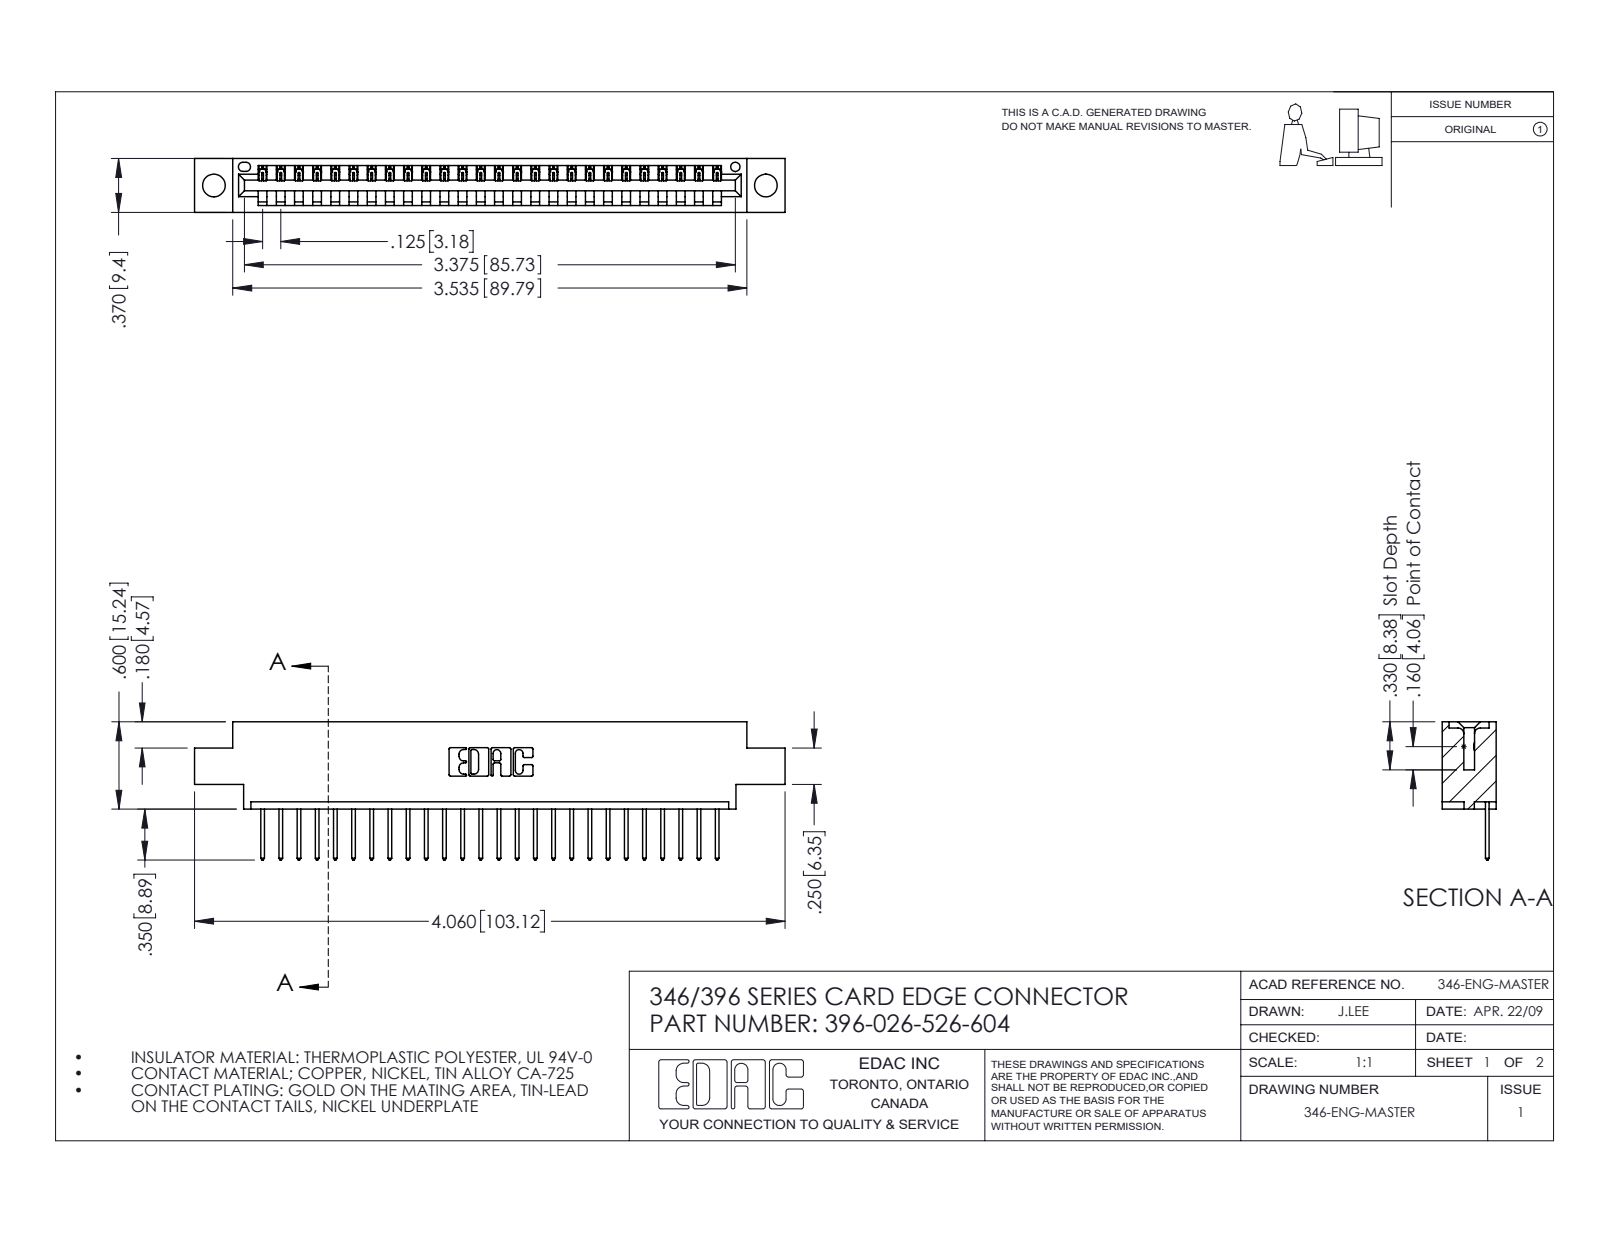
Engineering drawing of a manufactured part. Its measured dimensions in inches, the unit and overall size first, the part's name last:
Units: inches
Overall size (bounding box): 4.06 × 0.95 × 0.37
Round holes (diameter × count): ⌀0.156 ×2, ⌀0.064 ×1
Partial cylindrical surfaces — rounded edges, fillets, slot ends (radius × count): R0.006 ×52, R0.01 ×52, R0.01 ×22, R0.007 ×6, R0.031 ×6, R0.026 ×3, R0.031 ×2, R0.04 ×2
Main face-to-face distances: 0.048, 0.322, 0.37, 0.25, 0.072, 0.298, 0.025, 0.148, 0.222, 0.1
Hole centre spacings: 0.246, 3.587, 3.795
Volume: 0.58 in³ · Surface area: 18.04 in²
Bodies: 27 solids, 1634 faces (1120 planar, 514 cylindrical, 0 other)
Part name (STEP PRODUCT): 345-292-001_345-293-126; 346 Part_0.170 Offset - 0.156 Dia-TH; 396-026-526-604
STEP written by: SolidWorks 2016 (CONFIG_CONTROL_DESIGN)
